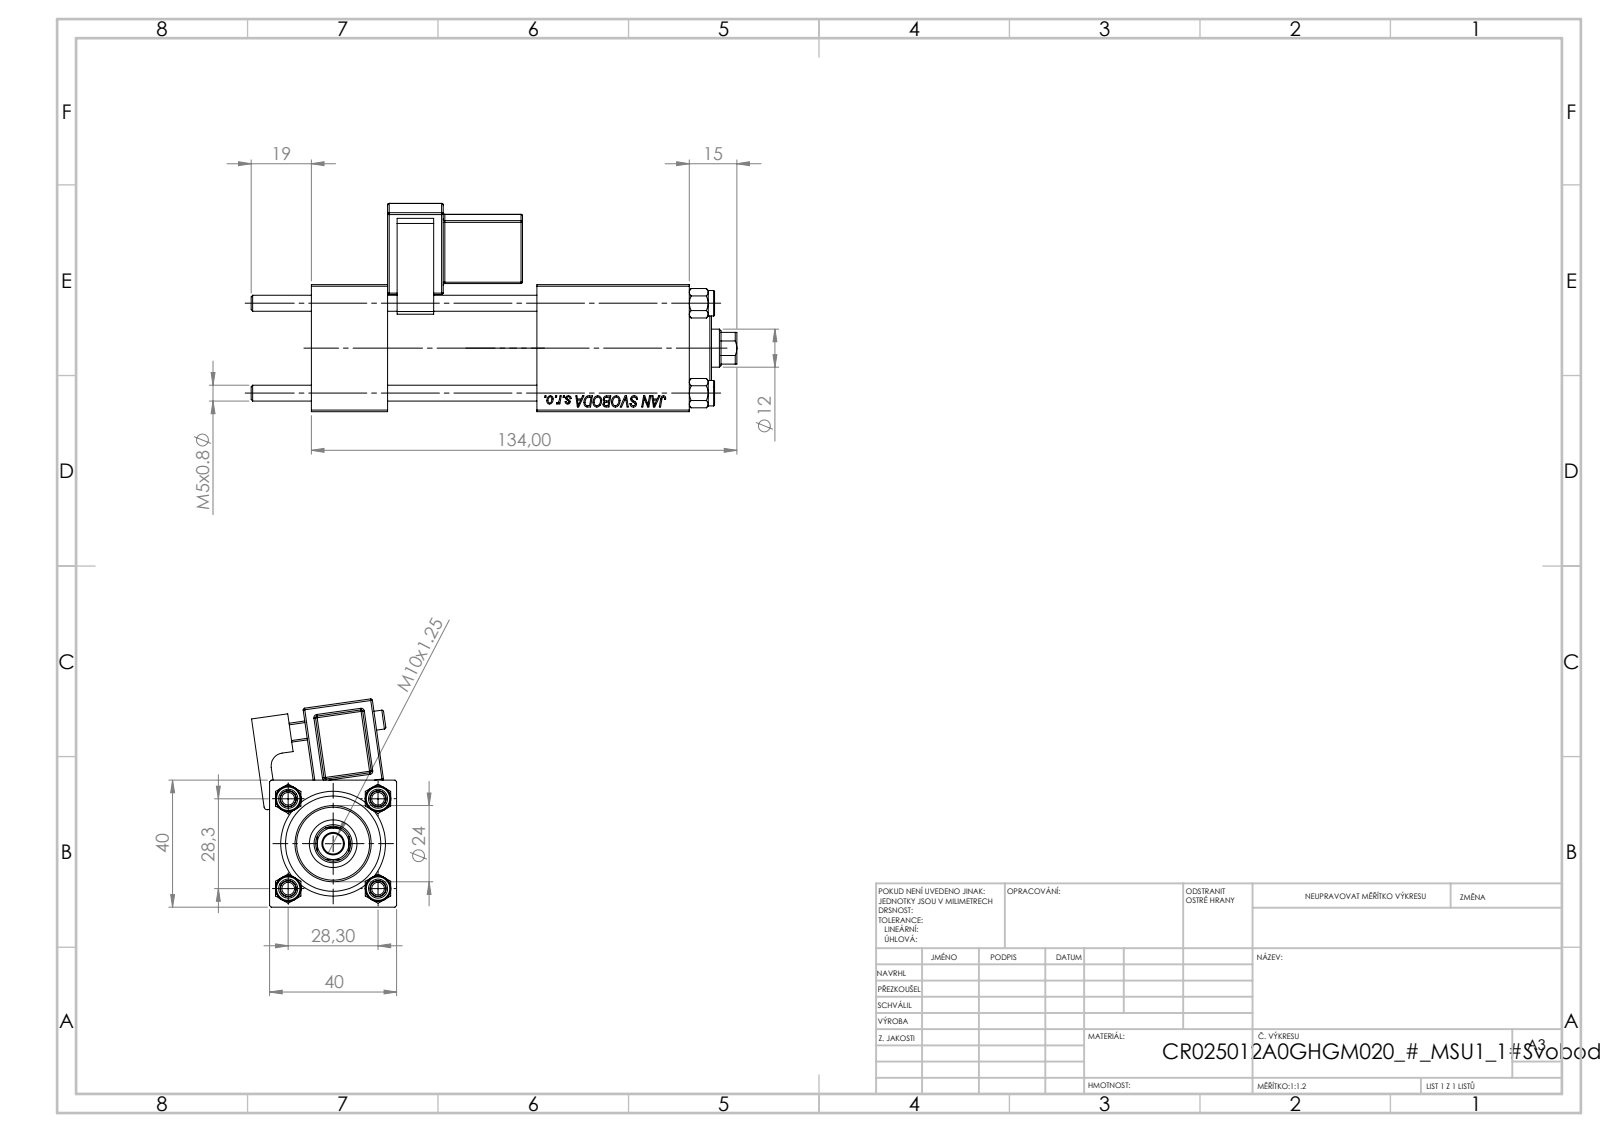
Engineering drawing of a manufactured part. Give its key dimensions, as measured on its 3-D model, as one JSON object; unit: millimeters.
{"part_name": "V215CR_BODY_A; V215_VC_A; CR025_012_A_0_G_A_G_M_020_+#_##_TYCINKA; NUT_M5 (+2 more)", "step_written_by": "SolidWorks 2019 (CONFIG_CONTROL_DESIGN)", "units": "millimeters", "bodies": {"solids": 12, "faces": 1210, "planar": 548, "cylindrical": 108, "other": 554}, "overall_size": [153, 65.59, 45.69], "volume_mm3": 165107, "surface_area_mm2": 64851, "round_holes": [[5, 4], [20, 3], [7, 2], [13.16, 2], [6.5, 1], [12, 1], [15, 1], [25, 1], [30, 1]], "round_bosses_or_shafts": [[8, 4], [31, 1], [24, 1], [6, 1]], "partial_cylinders_radius": [[0.5, 24], [1, 1], [2.5, 1], [4, 1], [5.5, 1]], "face_to_face_distances": [40, 24, 3, 119, 95, 90.3, 66.3, 28.7, 71, 47], "hole_center_spacings": [20.01, 28.3, 40.02, 72]}
